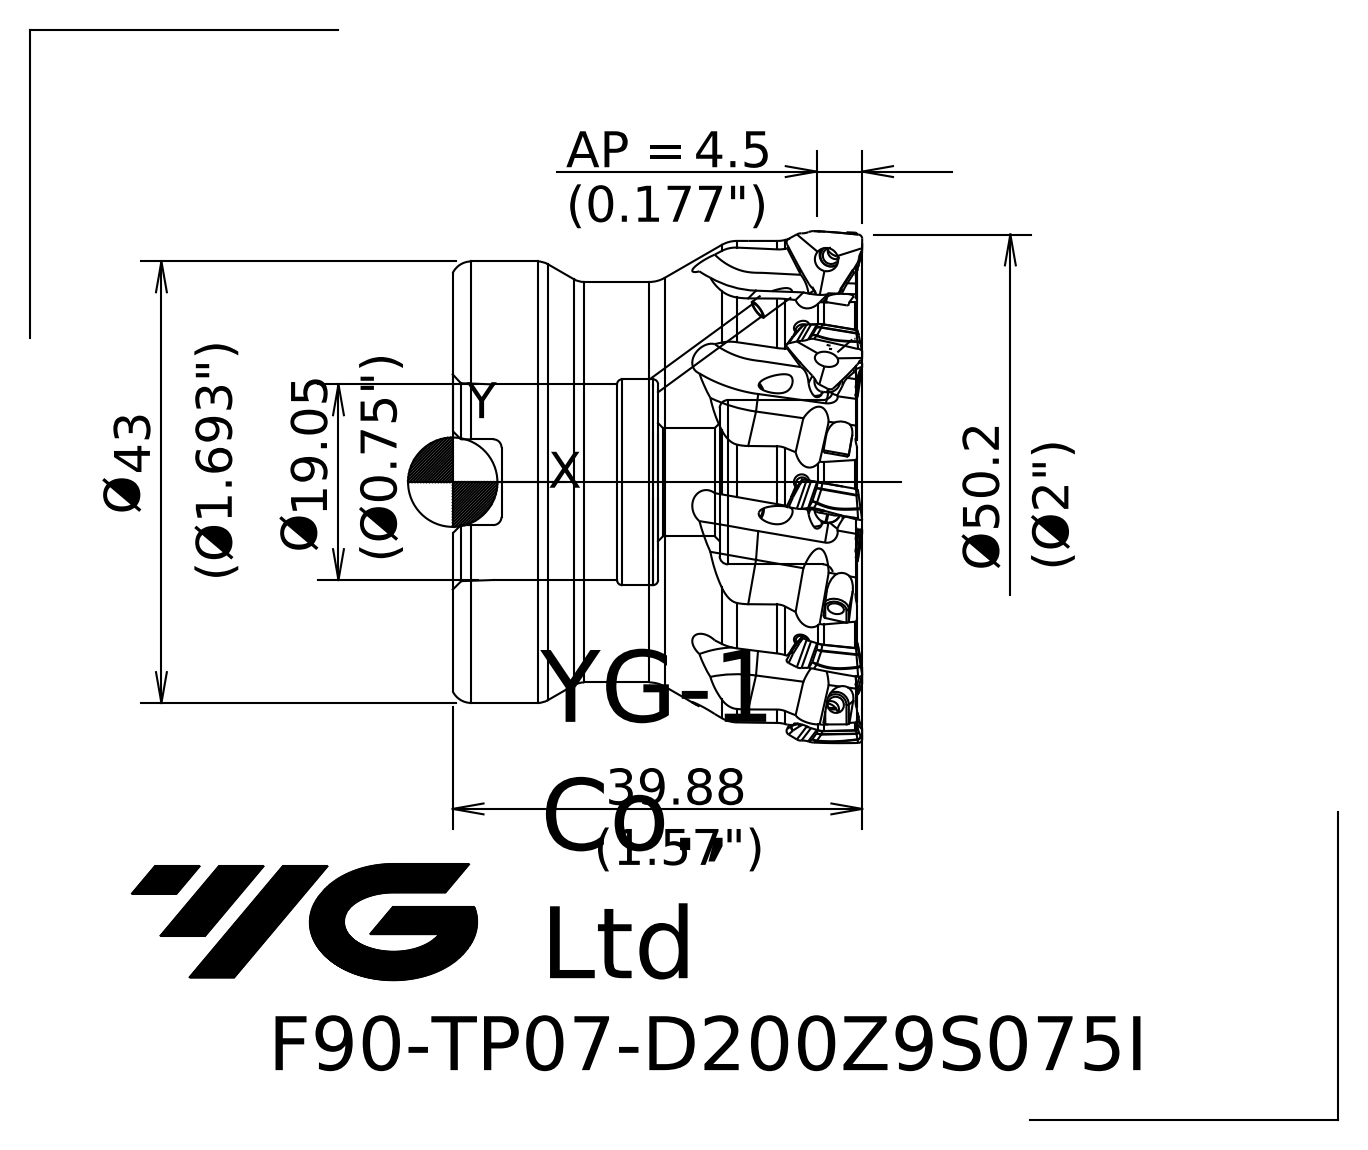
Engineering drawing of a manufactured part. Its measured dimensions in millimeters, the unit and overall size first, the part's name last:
Units: millimetres
Overall size (bounding box): 50.86 × 50.86 × 39.88
Round holes (diameter × count): ⌀10.5 ×1, ⌀16 ×1, ⌀19.05 ×1, ⌀20.05 ×1
Round bosses / shafts (diameter × count): ⌀47 ×1, ⌀43 ×1, ⌀39 ×1
Partial cylindrical surfaces — rounded edges, fillets, slot ends (radius × count): R0.8 ×2
Main face-to-face distances: 39.23, 19.23, 20, 34.48, 15.25, 4.75, 19.38, 34.63, 39.38, 8.35
Volume: 48 038 mm³ · Surface area: 13 880 mm²
Bodies: 1 solid, 75 faces (16 planar, 11 cylindrical, 48 other)
Part name (STEP PRODUCT): 10220ED003C8flwu
STEP written by: SIEMENS PLM Software NX 10.0 (AP203_CONFIGURATION_CONTROLLED_3D_DESIGN_OF_MECHANICAL_PARTS_AND_ASSEMBLIES_MIM_LF)
